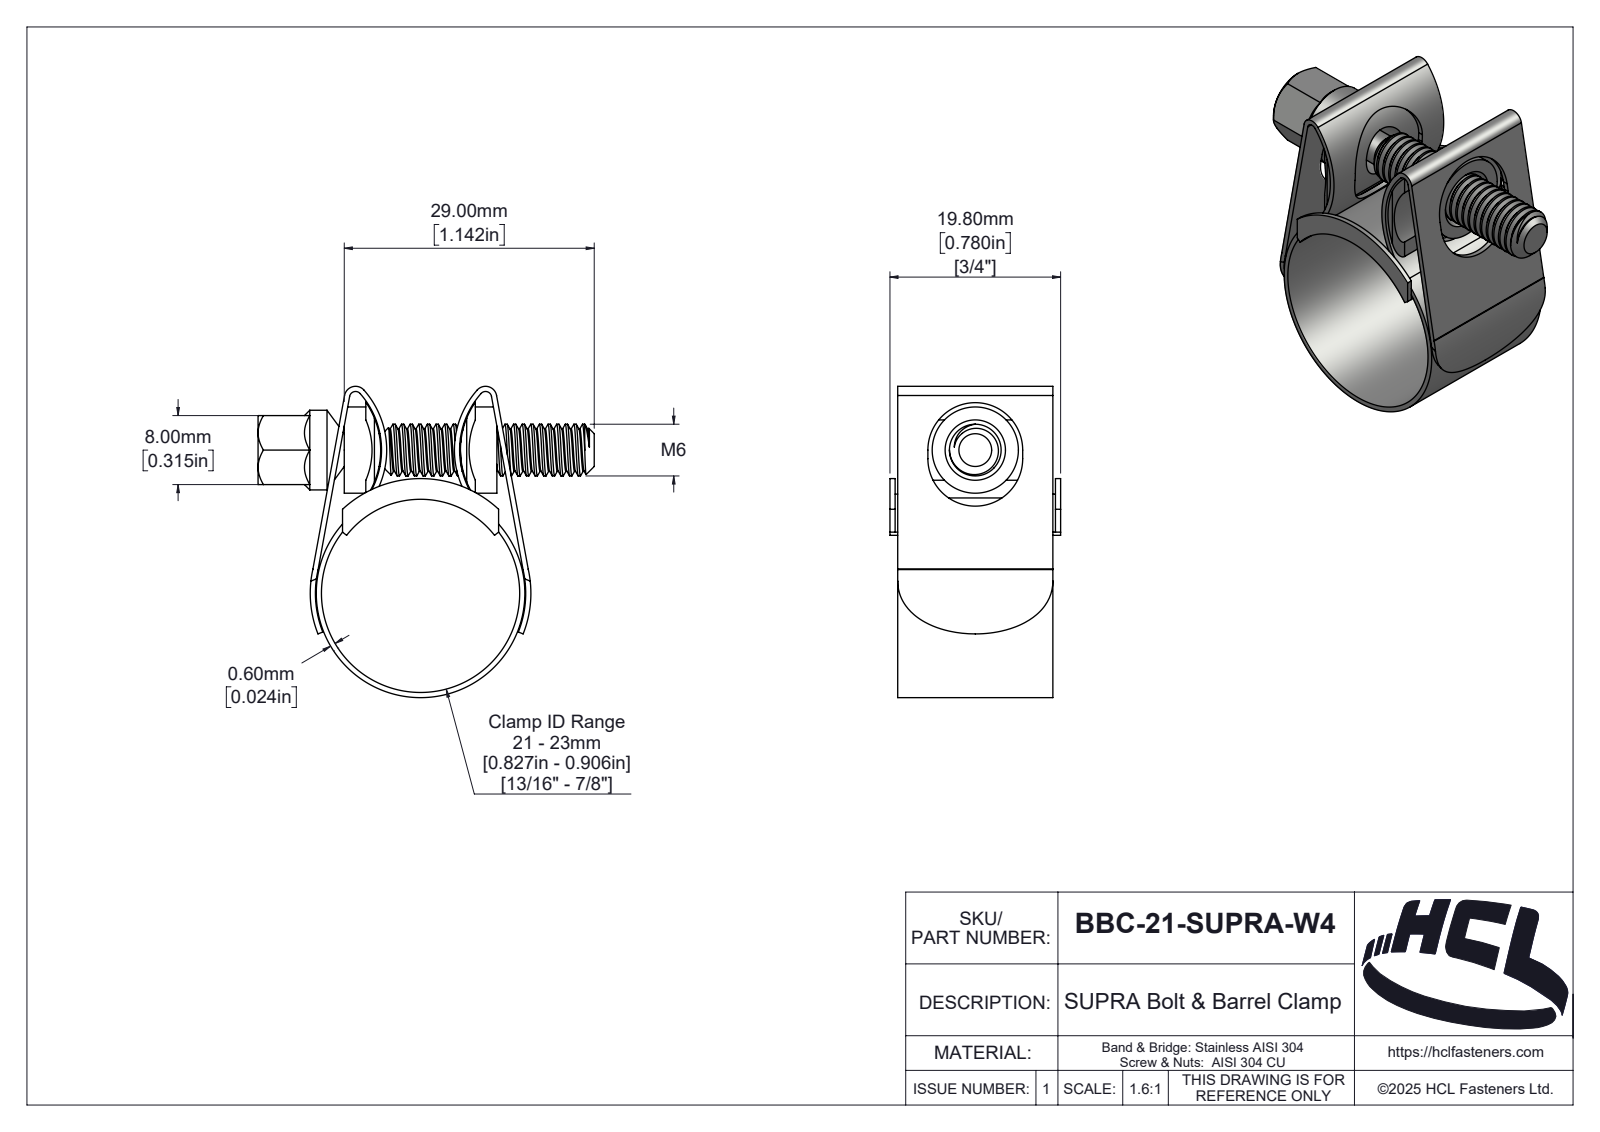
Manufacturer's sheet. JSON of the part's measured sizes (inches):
{"part_name": "BBC-21-SUPRA-W4", "step_written_by": "SolidWorks 2025 (AUTOMOTIVE_DESIGN)", "units": "inches", "bodies": {"solids": 5, "faces": 283, "planar": 44, "cylindrical": 159, "other": 80}, "overall_size": [1.535, 1.421, 0.78], "volume_in3": 0.203, "surface_area_in2": 12.15, "round_holes": [[0.906, 1]], "round_bosses_or_shafts": [[0.394, 1], [0.364, 1], [0.236, 1], [0.15, 1]], "partial_cylinders_radius": [[0.039, 4], [0.028, 2], [0.051, 2], [0.079, 2], [0.102, 2], [0.217, 2], [0.346, 2], [0.385, 2]], "face_to_face_distances": [0.024, 0.035, 0.744, 0.709, 0.098, 0.598, 0.315, 0.756, 0.72, 0.697]}
